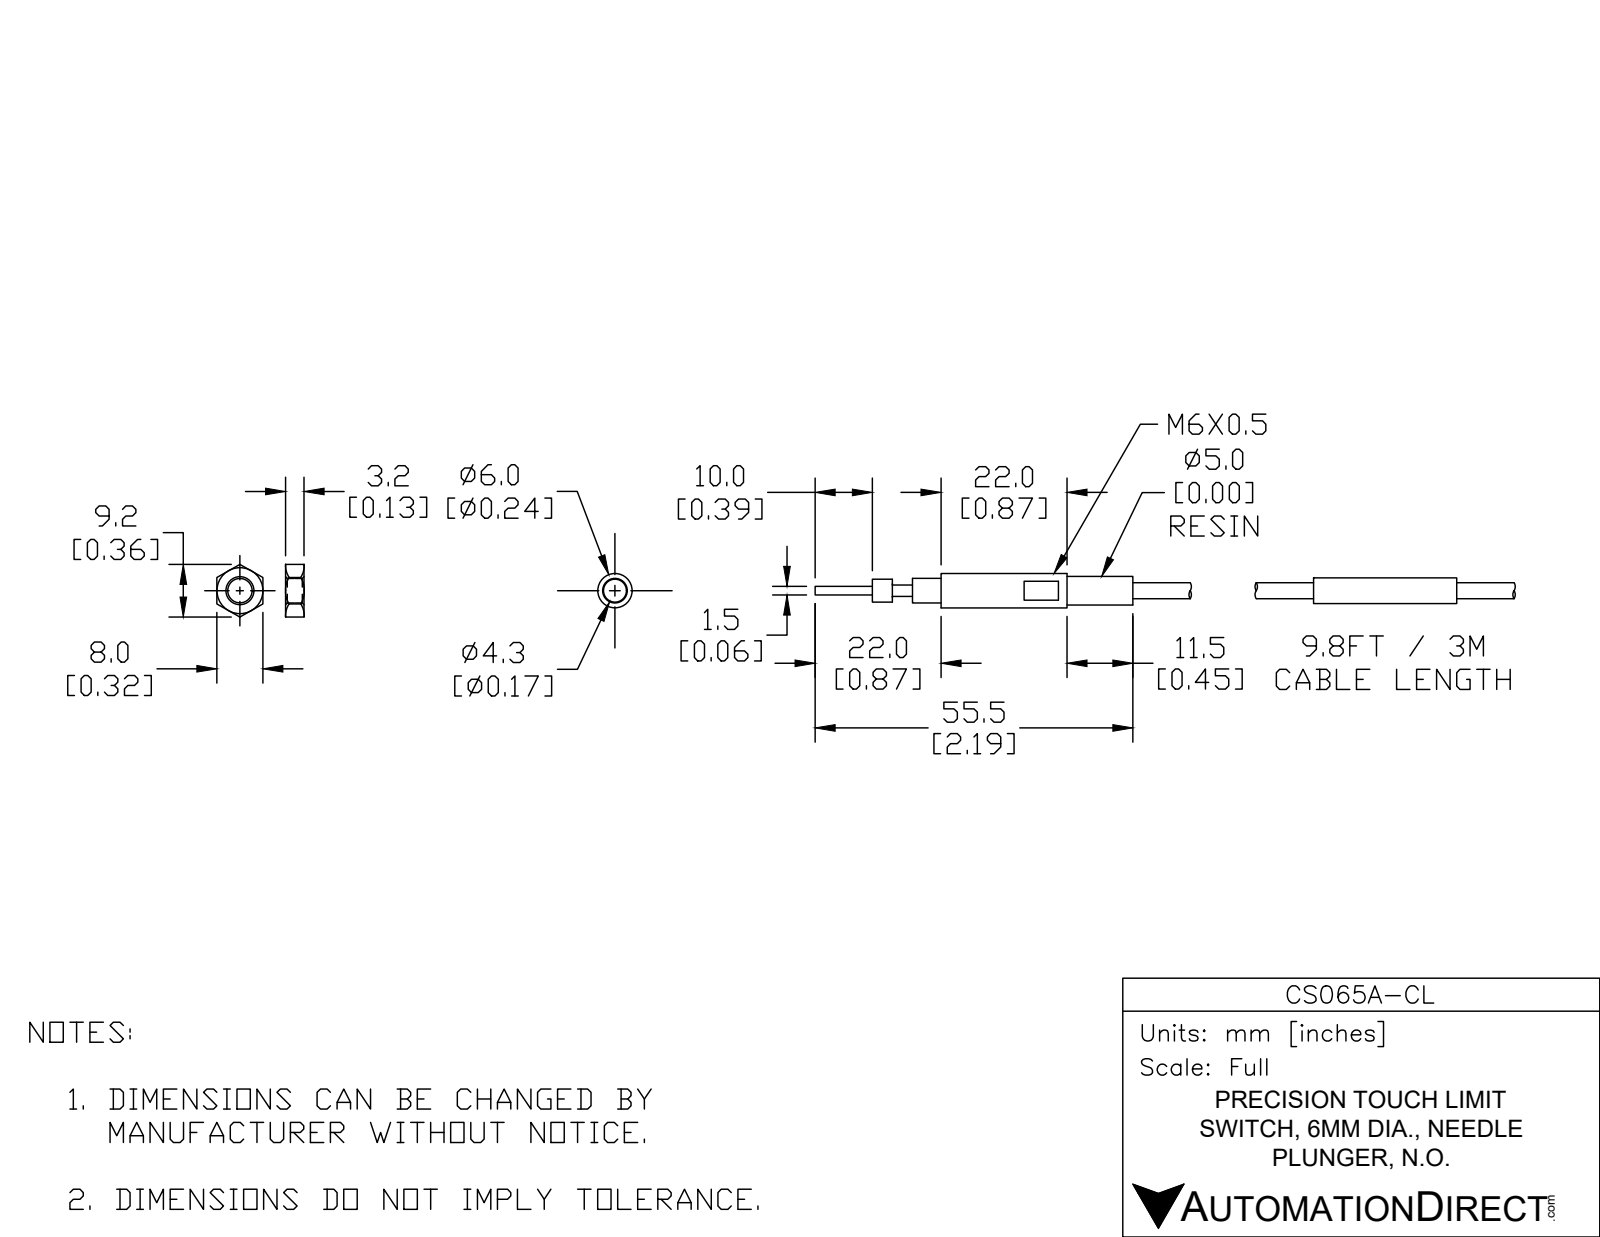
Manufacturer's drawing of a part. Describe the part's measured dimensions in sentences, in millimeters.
The part is named "CS065A-CL". Its 3-D file was written by "SolidWorks 2017 (AUTOMOTIVE_DESIGN)". It is 2 solids with 28 faces: 18 planar, 10 cylindrical and 0 other. Overall it measures 113.6 by 6.1 by 6.1 millimeters. Its volume is 1 600 cubic millimeters and its surface area 1 523 square millimeters. Round bosses or shafts: 1 of diameter 6.1, 1 of diameter 5, 1 of diameter 4.5, 1 of diameter 4.3, 1 of diameter 4, 1 of diameter 2.8, 1 of diameter 2, 1 of diameter 1.5. The main face-to-face distances are 5, 3.5, 33.6, 10.5, 12.5, 38.6, 7, 12, 45.6, 68.6.
